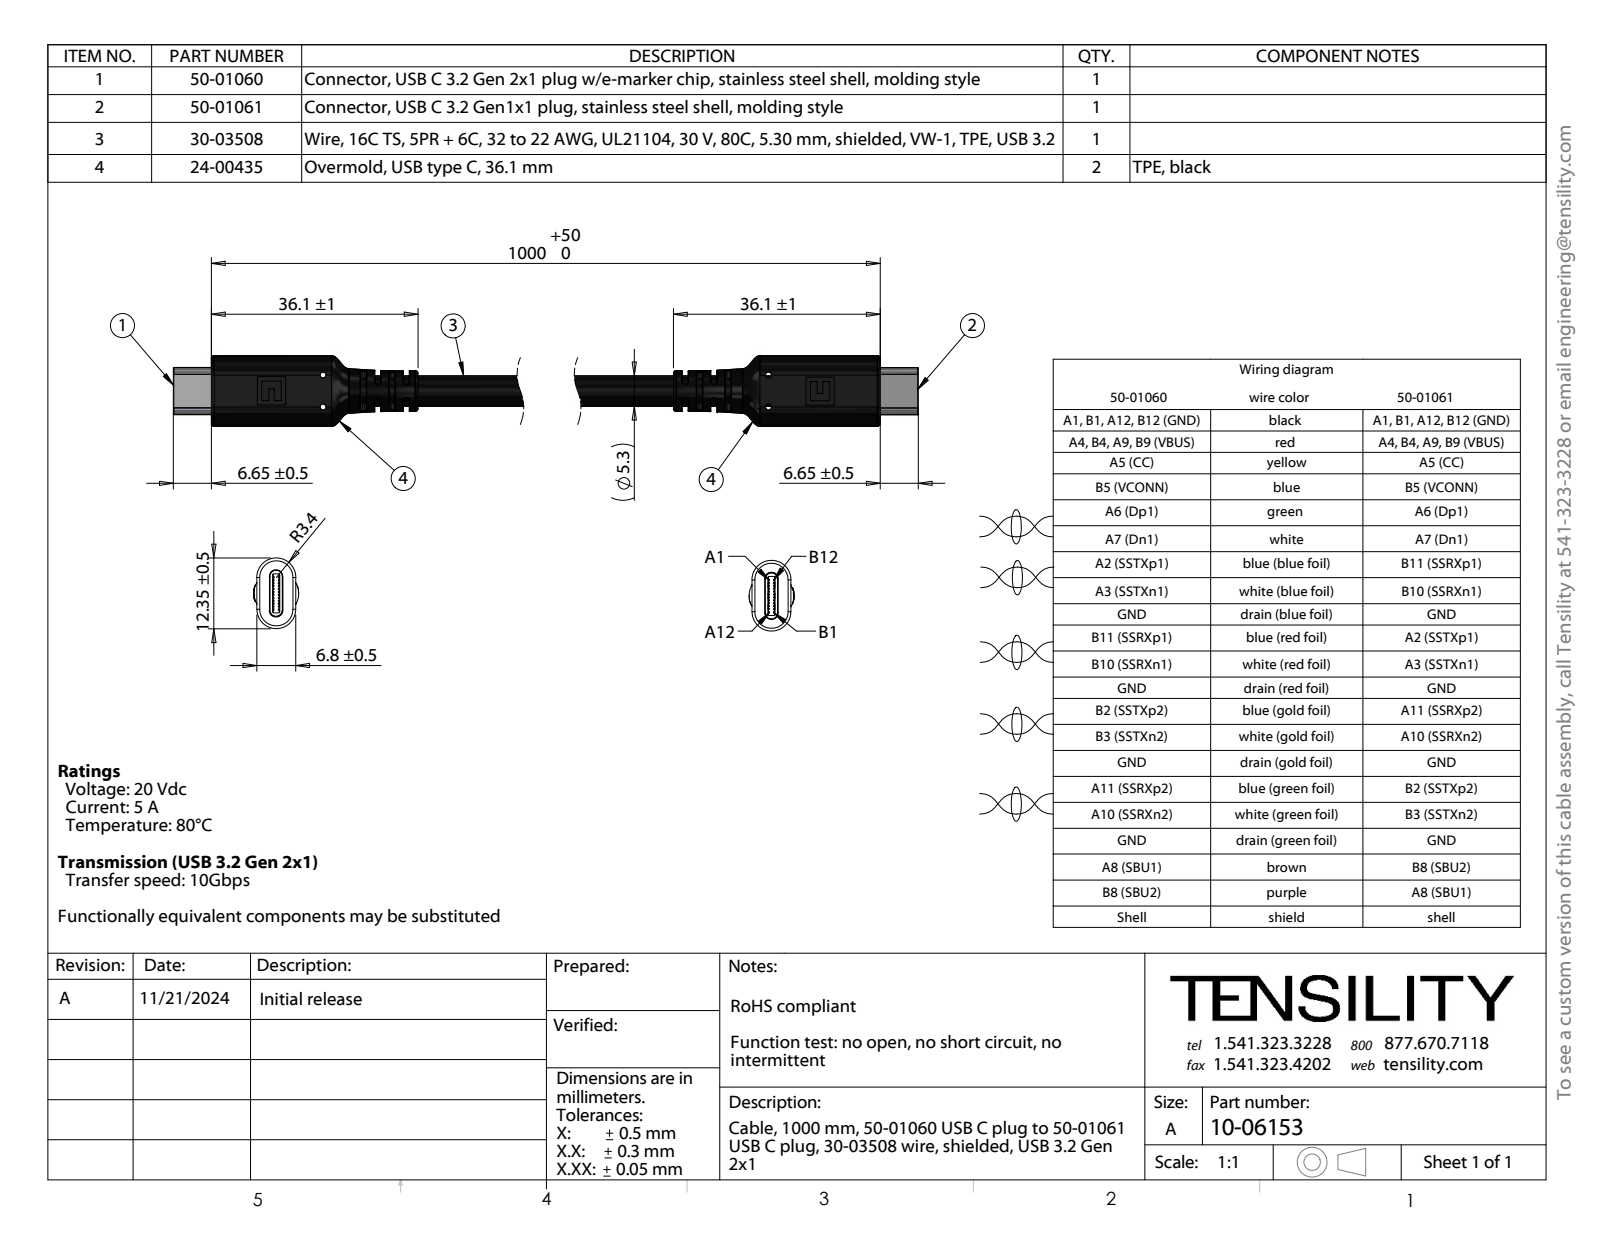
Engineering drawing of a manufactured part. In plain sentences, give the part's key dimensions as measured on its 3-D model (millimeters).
The part is named "10-06153; 50-01060; 30-03508; 50-01061_Hidden emarker (+1 more)". Its 3-D file was written by "SolidWorks 2021 (CONFIG_CONTROL_DESIGN)". It is 168 solids with 1726 faces: 728 planar, 766 cylindrical and 232 other. Overall it measures 208.34 by 12.35 by 7.89 millimeters. Its volume is 6 767 cubic millimeters and its surface area 49 412 square millimeters. Round holes: 4 of diameter 1, 1 of diameter 4.16, 1 of diameter 4.17, 1 of diameter 4.19, 1 of diameter 4.2, 1 of diameter 4.4. Round bosses or shafts: 8 of diameter 0.74, 4 of diameter 0.48, 4 of diameter 0.25, 2 of diameter 0.55, 1 of diameter 7.82, 1 of diameter 5.3, 1 of diameter 1, 1 of diameter 0.9. Partial cylindrical surfaces (rounded edges, fillets, slot ends): 20 of radius 0.5, 8 of radius 0.25, 4 of radius 0.1, 4 of radius 0.15, 4 of radius 1.18, 2 of radius 0.3, 2 of radius 0.31, 2 of radius 0.47. The main face-to-face distances are 1.04, 1.05, 1.03, 0.95, 1.1, 6.8, 0.62, 0.63, 2.35, 1.4. The hole center spacings are 2.11, 2.07, 0.64, 2.14, 0.62, 2.02, 2.05, 2.46.
